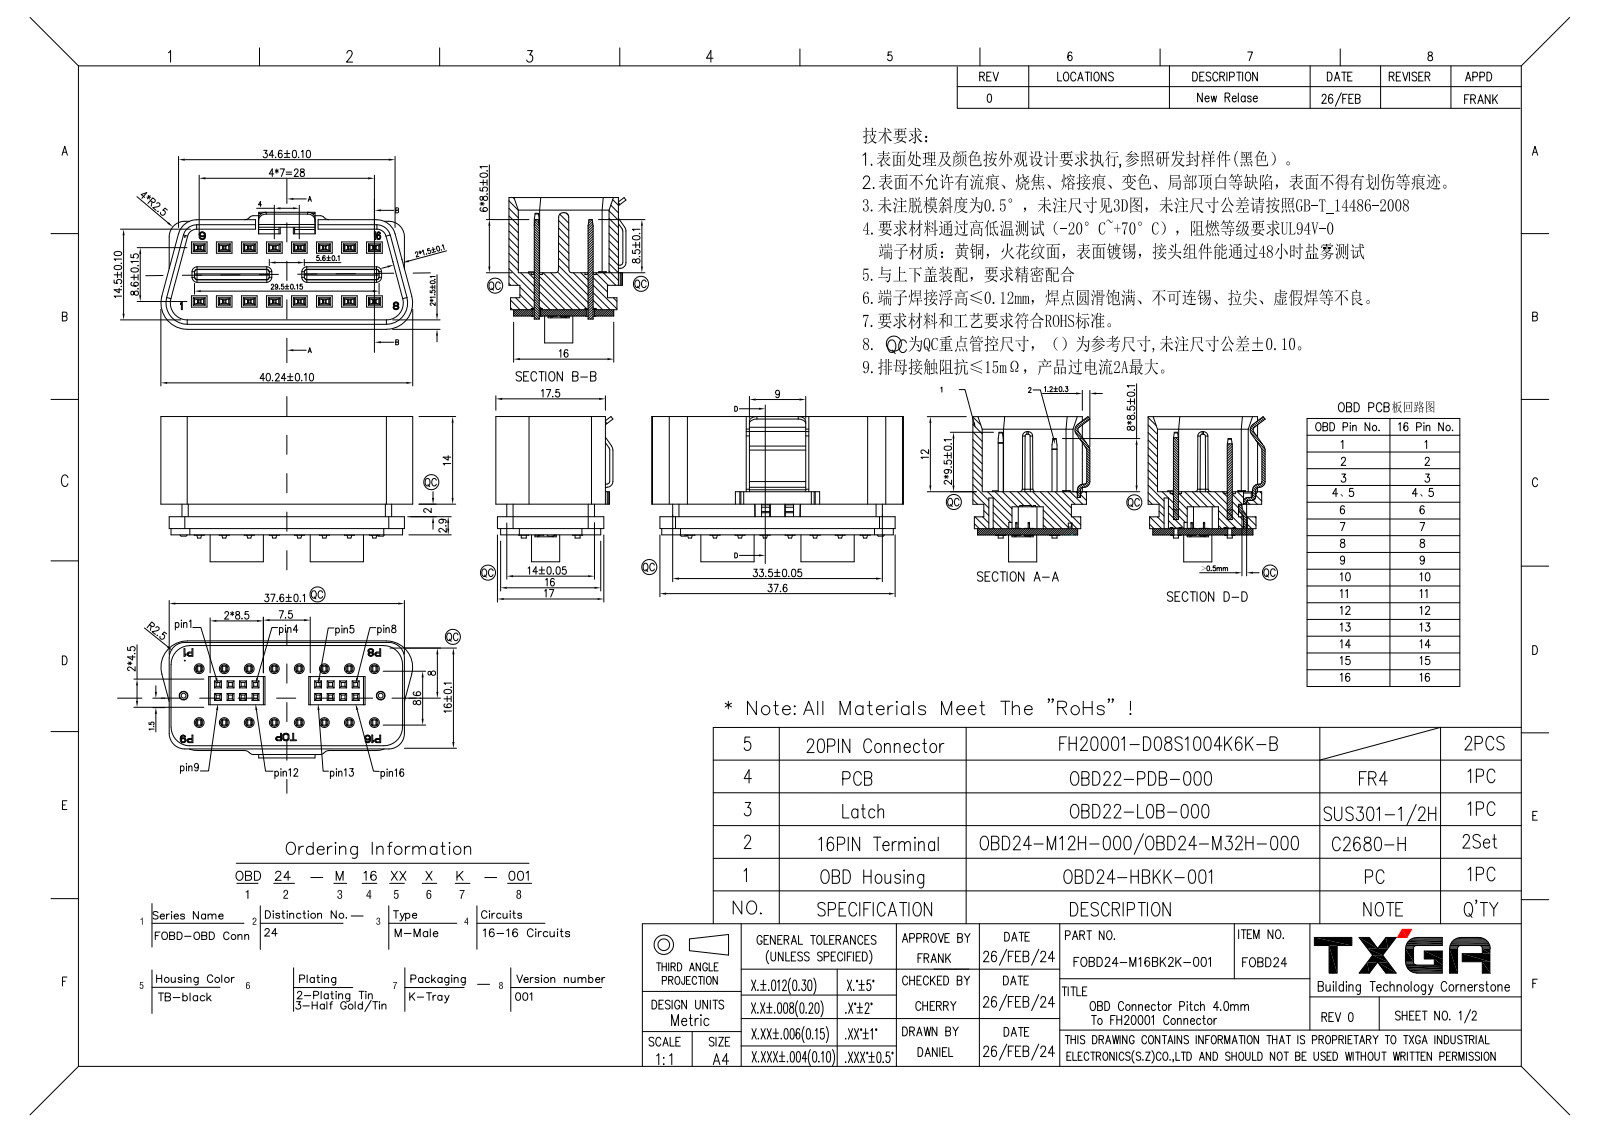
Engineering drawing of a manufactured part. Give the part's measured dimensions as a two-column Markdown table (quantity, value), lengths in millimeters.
| quantity | value |
| --- | --- |
| part name | HOUSING22337046T; PIN9; WAN-PIN37046T; PCB22337046T (+3 more) |
| STEP written by | PRO/ENGINEER BY PARAMETRIC TECHNOLOGY CORPORATION, 2010280 (CONFIG_CONTROL_DESIGN) |
| units | millimeters |
| bodies | 21 solids, 2150 faces (1619 planar, 507 cylindrical, 24 other) |
| overall size | 40.24 × 23.2 × 18.7 |
| volume | 5 771 mm³ |
| surface area | 9 650 mm² |
| round holes (diameter × count) | 0.9 × 16, 1.2 × 16, 1.4 × 2, 2.5 × 1 |
| round bosses / shafts (diameter × count) | 1.6 × 16, 1.4 × 16, 1.3 × 2 |
| partial cylindrical surfaces (radius × count) | 0.1 × 64, 0.15 × 36, 0.2 × 32, 0.4 × 21, 1 × 12, 0.3 × 6, 3 × 6, 0.5 × 4 |
| main face-to-face distances | 1.5, 0.8, 16, 13.45, 1, 2.55, 4.05, 4, 4.85, 2.3 |
| hole center spacings | 4, 9.48, 8, 11.75, 2, 12, 16, 14.76 |
